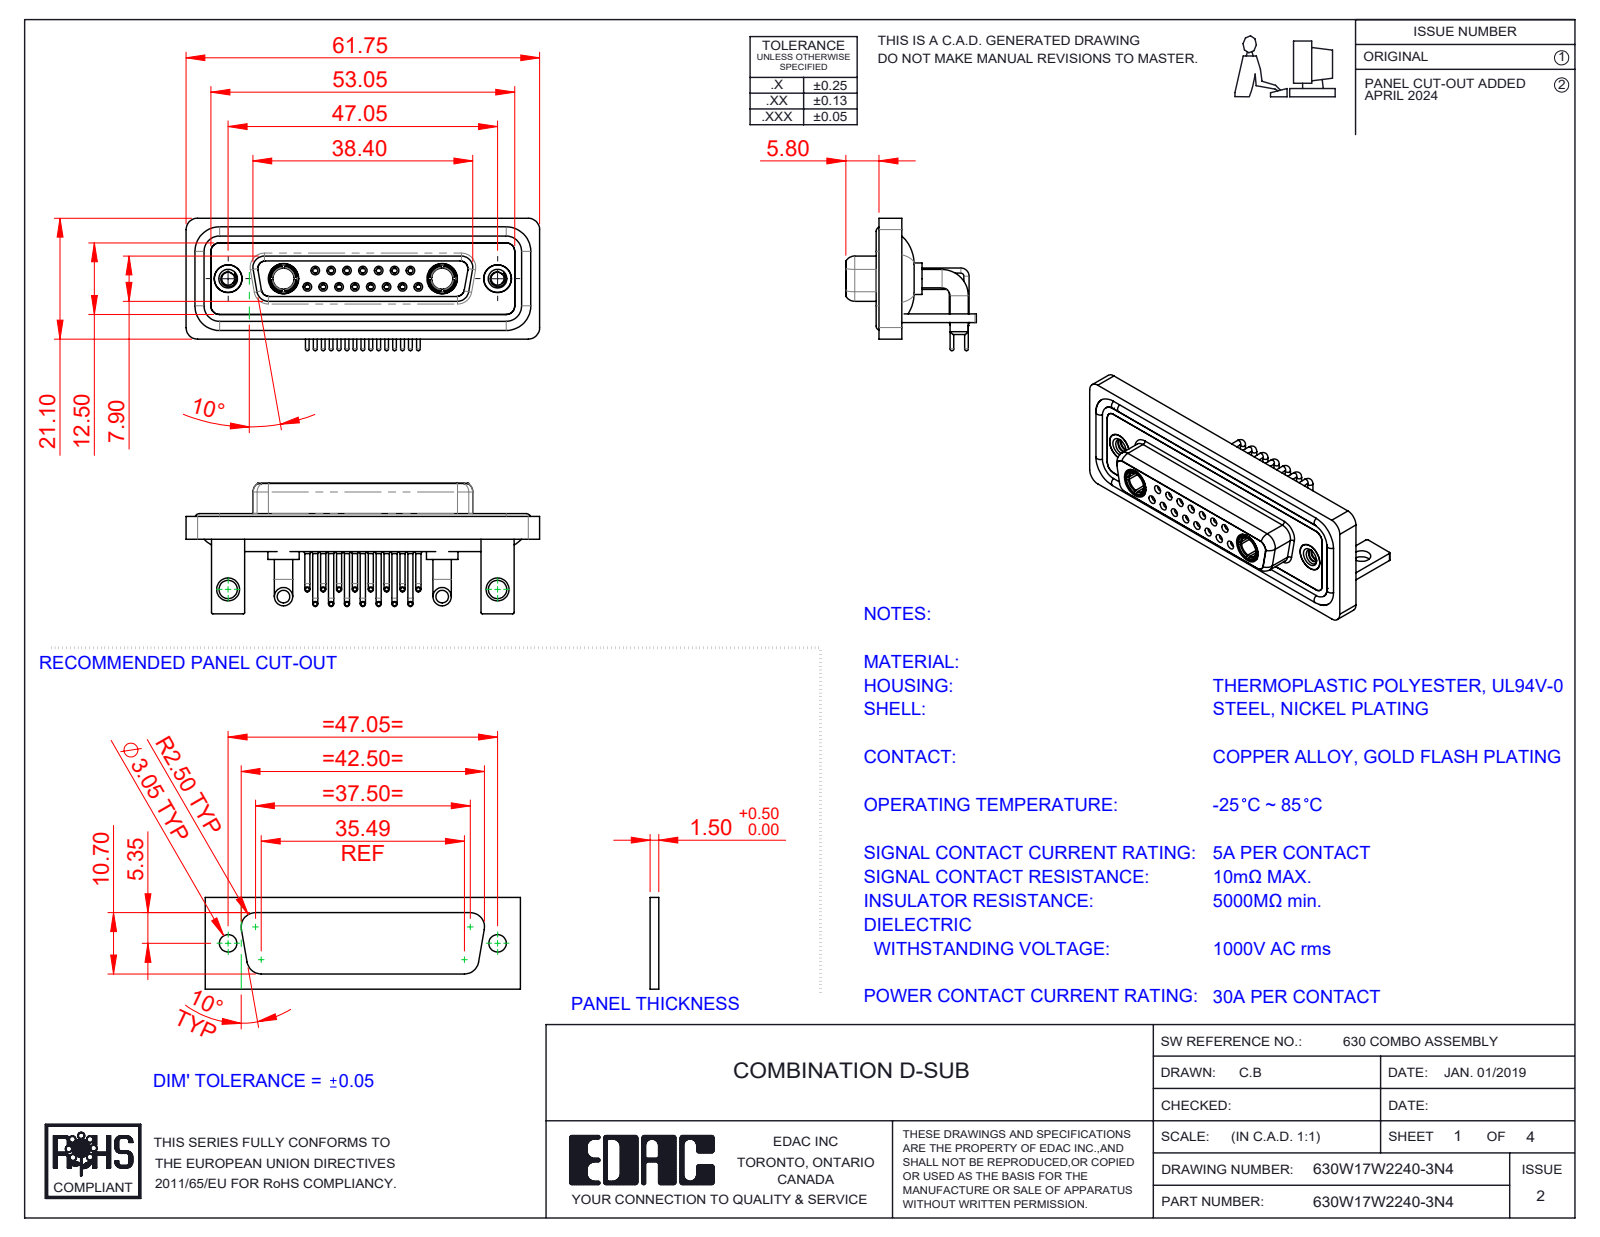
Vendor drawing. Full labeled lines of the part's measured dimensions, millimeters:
Part name (STEP PRODUCT): 630Combo Shell Front_25 Contacts; 630Combo Waterproof Housing_25 Contacts; 630Combo Shell Rear_25 Contacts; Power Socket_30A RA (+6 more)
STEP written by: SolidWorks 2023 (CONFIG_CONTROL_DESIGN)
Units: millimetres
Bodies: 28 solids, 1385 faces (408 planar, 607 cylindrical, 370 other)
Overall size (bounding box): 61.75 × 23.12 × 22.8
Volume: 8 909 mm³ · Surface area: 15 302 mm²
Round holes (diameter × count): ⌀0.9 ×15, ⌀1.1 ×15, ⌀1.5 ×15, ⌀2 ×15, ⌀1.6 ×8, ⌀1.7 ×7, ⌀4.85 ×4, ⌀2.26 ×2, ⌀3.2 ×2, ⌀3.7 ×2, ⌀4 ×2, ⌀4.05 ×2
Round bosses / shafts (diameter × count): ⌀0.9 ×15, ⌀0.65 ×15, ⌀1.6 ×11, ⌀3.2 ×4, ⌀5.5 ×2, ⌀5.2 ×2, ⌀4.96 ×2, ⌀4.95 ×2
Partial cylindrical surfaces — rounded edges, fillets, slot ends (radius × count): R2 ×19, R1.5 ×18, R0.25 ×16, R1.35 ×8, R1.6 ×8, R0.5 ×5, R0.6 ×4, R0.65 ×4
Main face-to-face distances: 0.4, 1.8, 2.9, 3.7, 1.5, 4.1, 1.1, 1.4, 1.6, 3.1
Hole centre spacings: 3.16, 2.77, 5.54, 8.31, 5.04, 7.49, 11.08, 5.03
